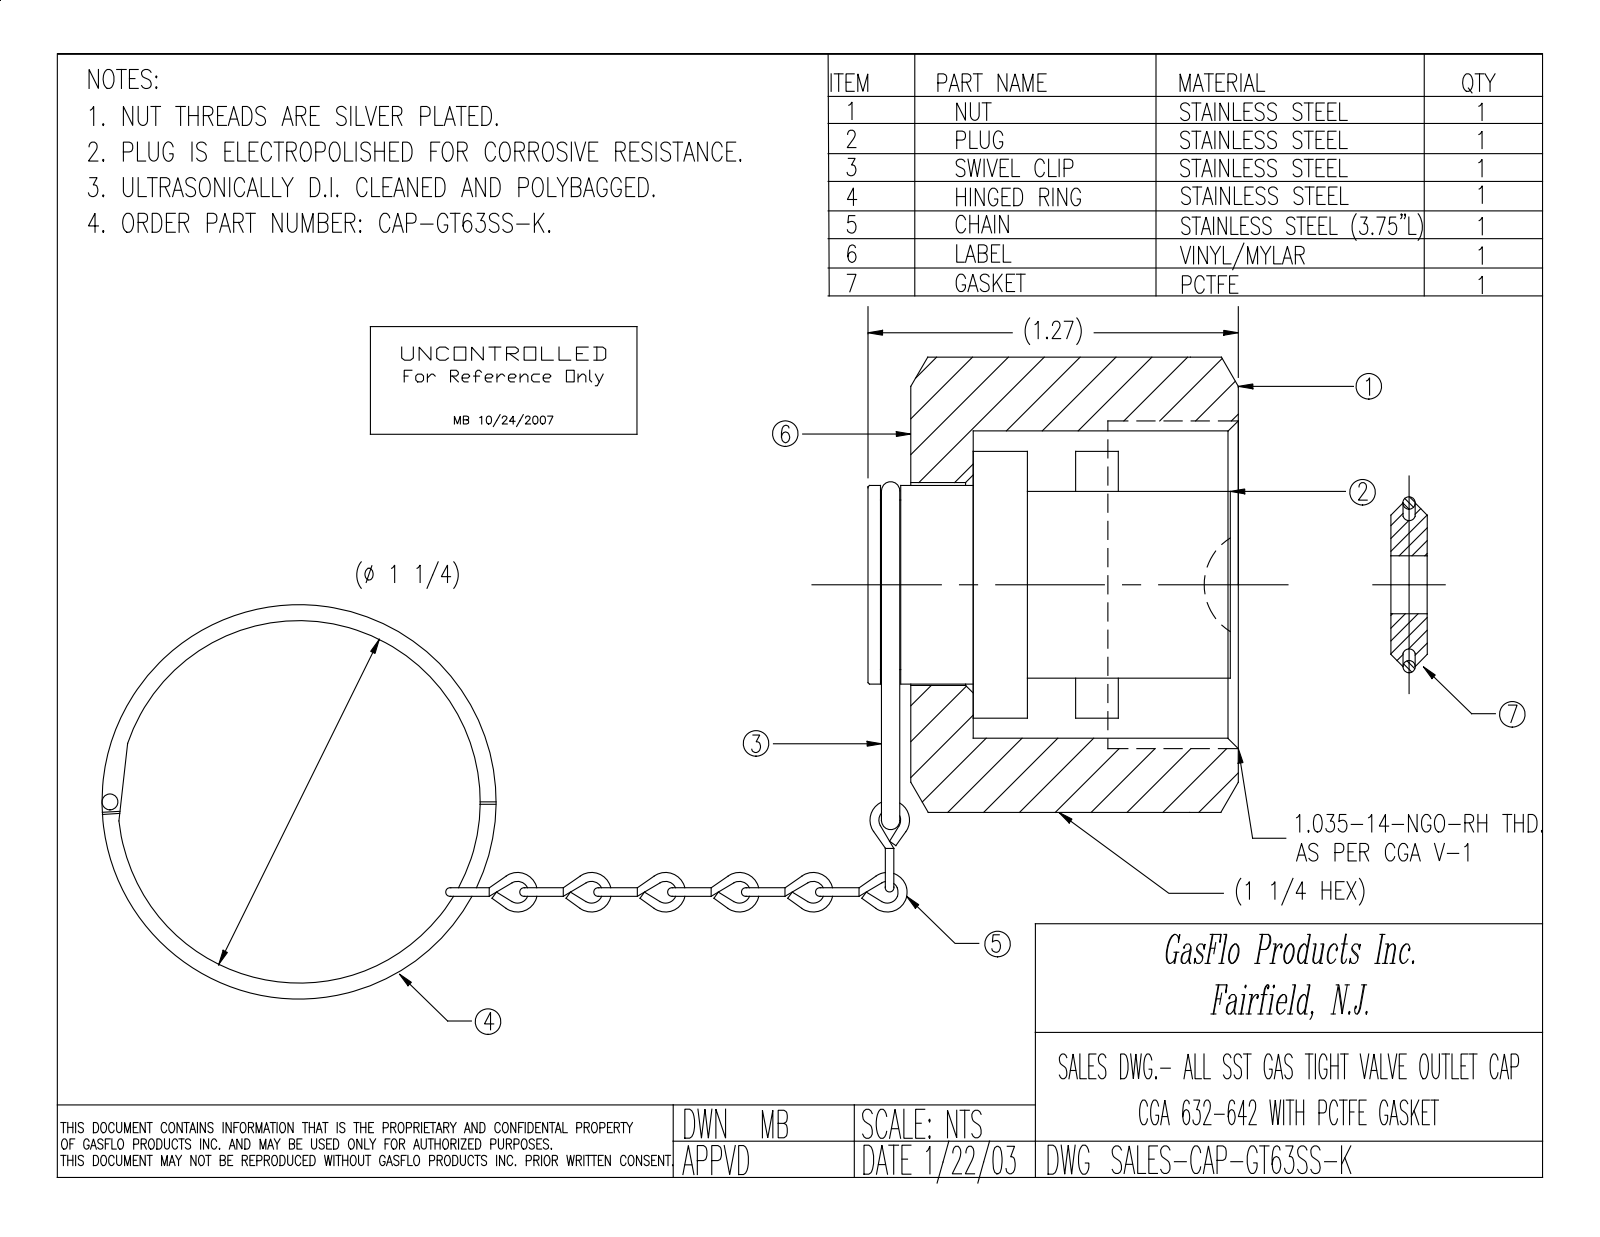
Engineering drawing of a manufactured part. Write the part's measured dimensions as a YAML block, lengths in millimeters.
part_name: "PRT-002245_RING-1.187D HALF; PRT-002239_STAINLESS; ASY-000691; PRT-002255_SMALL PIN (+8 more)"
step_written_by: "SolidWorks 2018 (CONFIG_CONTROL_DESIGN)"
units: millimeters
bodies: {solids: 17, faces: 975, planar: 488, cylindrical: 174, other: 313}
overall_size: [133.8, 52.4, 31.8]
volume: 21570
surface_area: 14660
round_holes:
  - {diameter: 1.6, count: 1}
  - {diameter: 2, count: 1}
  - {diameter: 3.8, count: 1}
  - {diameter: 5.4, count: 1}
  - {diameter: 8.5, count: 1}
  - {diameter: 14.7, count: 1}
  - {diameter: 17.7, count: 1}
  - {diameter: 19.6, count: 1}
  - {diameter: 24.4, count: 1}
round_bosses_or_shafts:
  - {diameter: 1.6, count: 32}
  - {diameter: 29.2, count: 1}
  - {diameter: 23.4, count: 1}
  - {diameter: 17.4, count: 1}
  - {diameter: 16.4, count: 1}
  - {diameter: 14.9, count: 1}
  - {diameter: 14.3, count: 1}
  - {diameter: 12.8, count: 1}
partial_cylinders:
  - {radius: 0.1, count: 24}
  - {radius: 6.4, count: 4}
  - {radius: 0.3, count: 2}
  - {radius: 4.8, count: 1}
face_to_face_distances: [31.8, 31.8, 3.6, 3.4, 32.3, 28.9, 28.7, 14, 10.6, 10.4]
